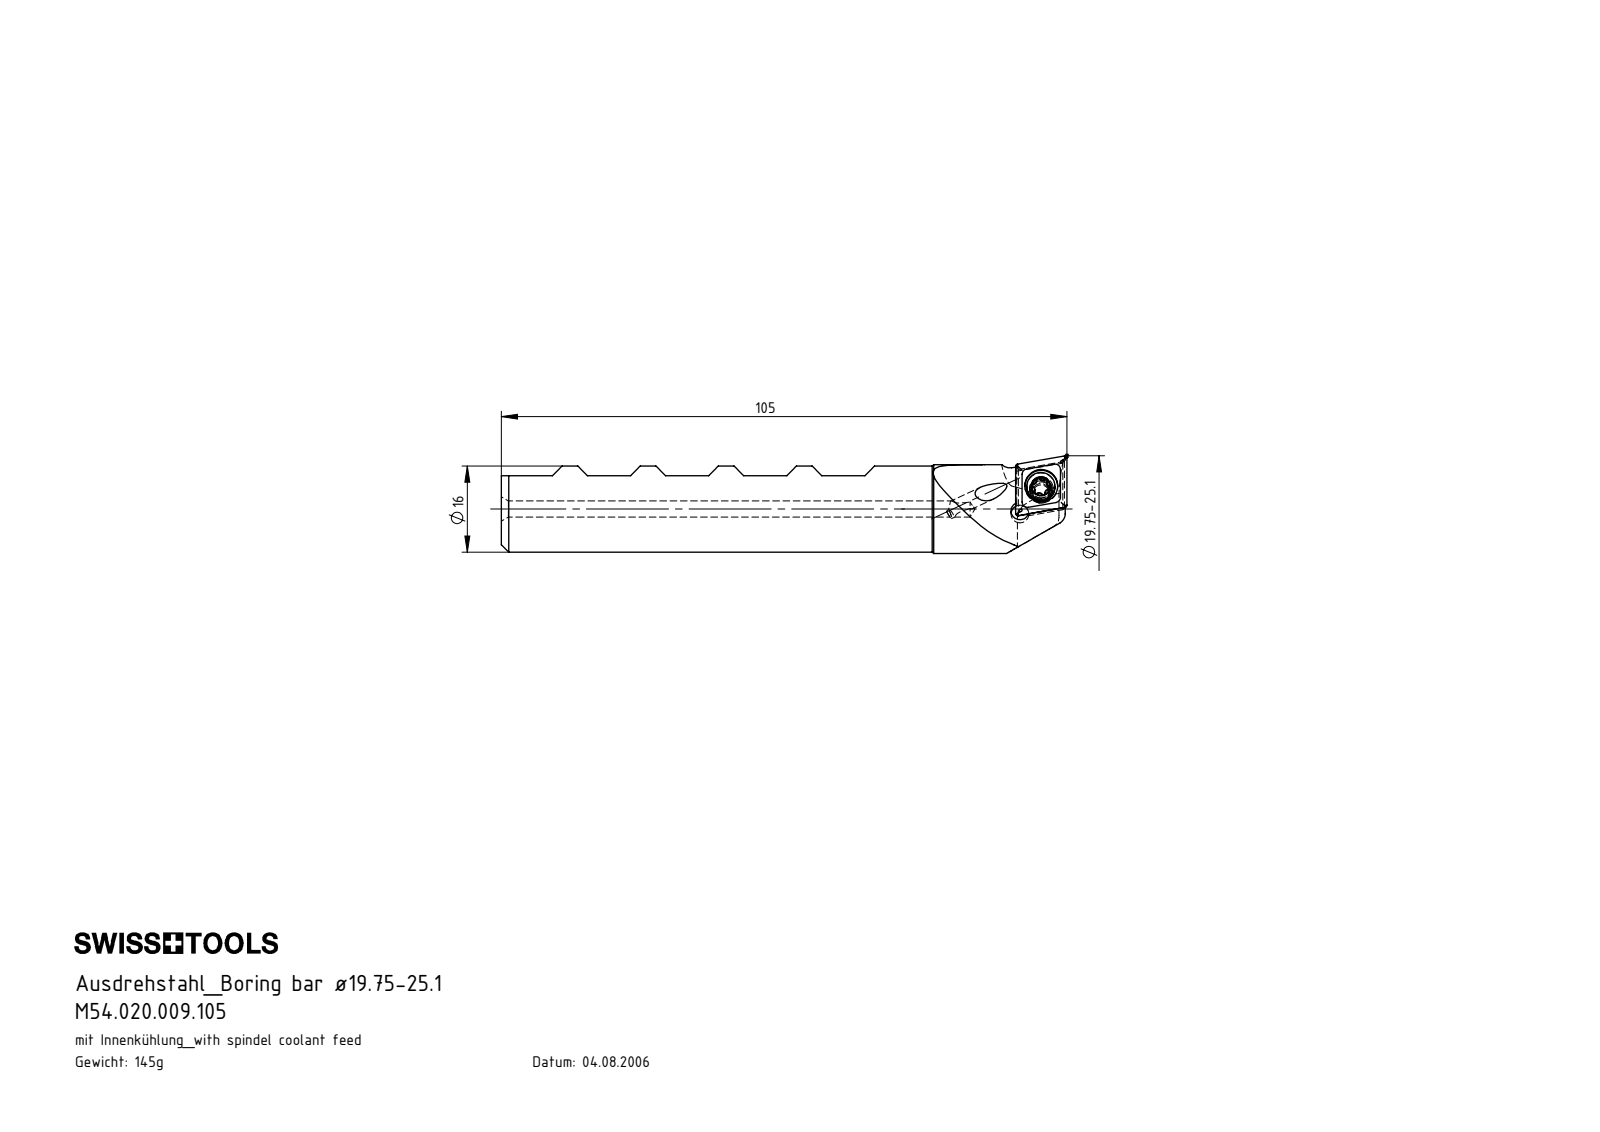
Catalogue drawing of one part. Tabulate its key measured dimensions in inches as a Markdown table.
| quantity | value |
| --- | --- |
| part name | WCB-ER2.001.009_A; CCMT09T304; B20.WCB.K11.105; B20-WCB.K11.105_B |
| STEP written by | SolidWorks 2017 (AUTOMOTIVE_DESIGN) |
| units | inches |
| bodies | 3 solids, 120 faces (45 planar, 28 cylindrical, 47 other) |
| overall size | 4.134 × 0.713 × 0.675 |
| volume | 1.123 in³ |
| surface area | 10.6 in² |
| round holes (diameter × count) | 0.118 × 2, 0.13 × 2, 0.173 × 1, 0.24 × 1 |
| round bosses / shafts (diameter × count) | 0.65 × 1, 0.63 × 1, 0.207 × 1, 0.157 × 1 |
| partial cylindrical surfaces (radius × count) | 0.013 × 6, 0.023 × 6, 0.079 × 1, 0.331 × 1, 0.374 × 1, 0.394 × 1 |
| main face-to-face distances | 0.404, 0.807, 0.807, 1.211, 0.148, 0.148, 0.156, 0.156, 0.228, 0.229 |
| hole center spacings | 0.239, 0.244 |
